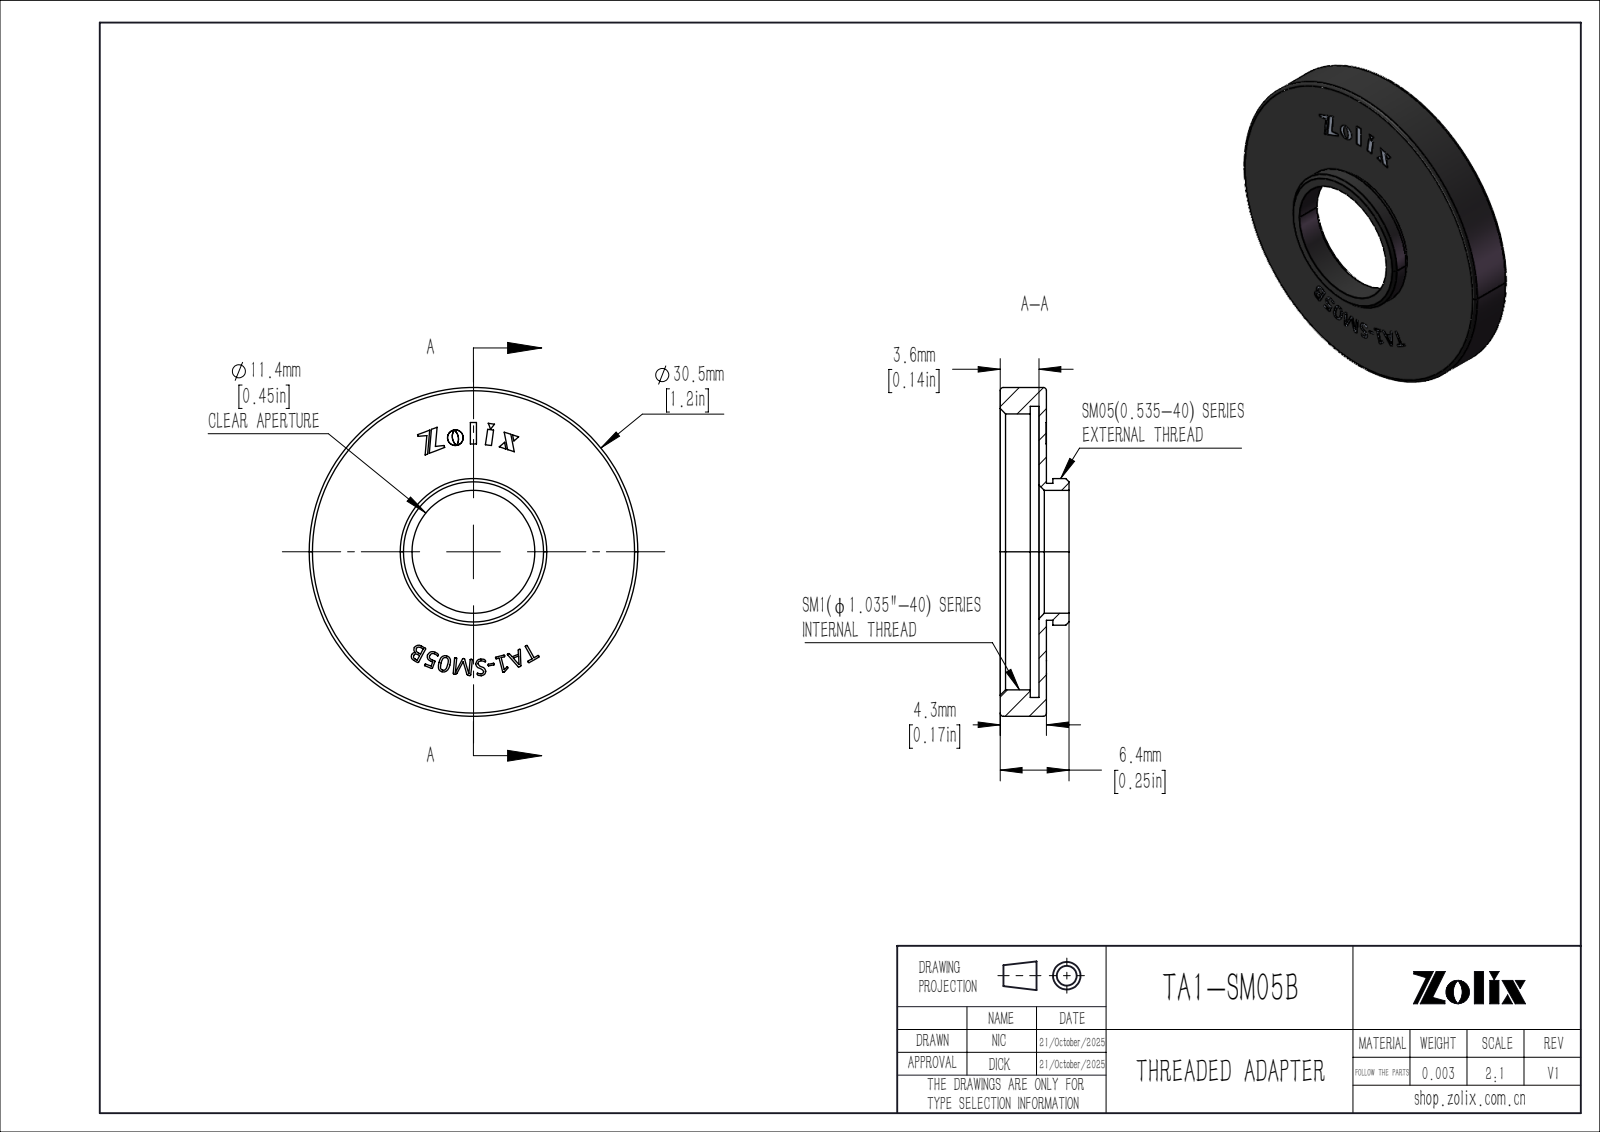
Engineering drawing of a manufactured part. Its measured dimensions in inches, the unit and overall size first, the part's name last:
Units: inches
Overall size (bounding box): 1.201 × 1.201 × 0.252
Round holes (diameter × count): ⌀0.449 ×1, ⌀1.008 ×1, ⌀1.063 ×1
Round bosses / shafts (diameter × count): ⌀1.201 ×1, ⌀0.535 ×1, ⌀0.5 ×1
Main face-to-face distances: 0.028, 0.142, 0.169, 0.11, 0.059, 0.031, 0.083, 0.252, 0.024, 0.051
Volume: 0.075 in³ · Surface area: 3.472 in²
Bodies: 1 solid, 330 faces (223 planar, 12 cylindrical, 95 other)
Part name (STEP PRODUCT): TA1-SM05B
STEP written by: SolidWorks 2020 (CONFIG_CONTROL_DESIGN)
